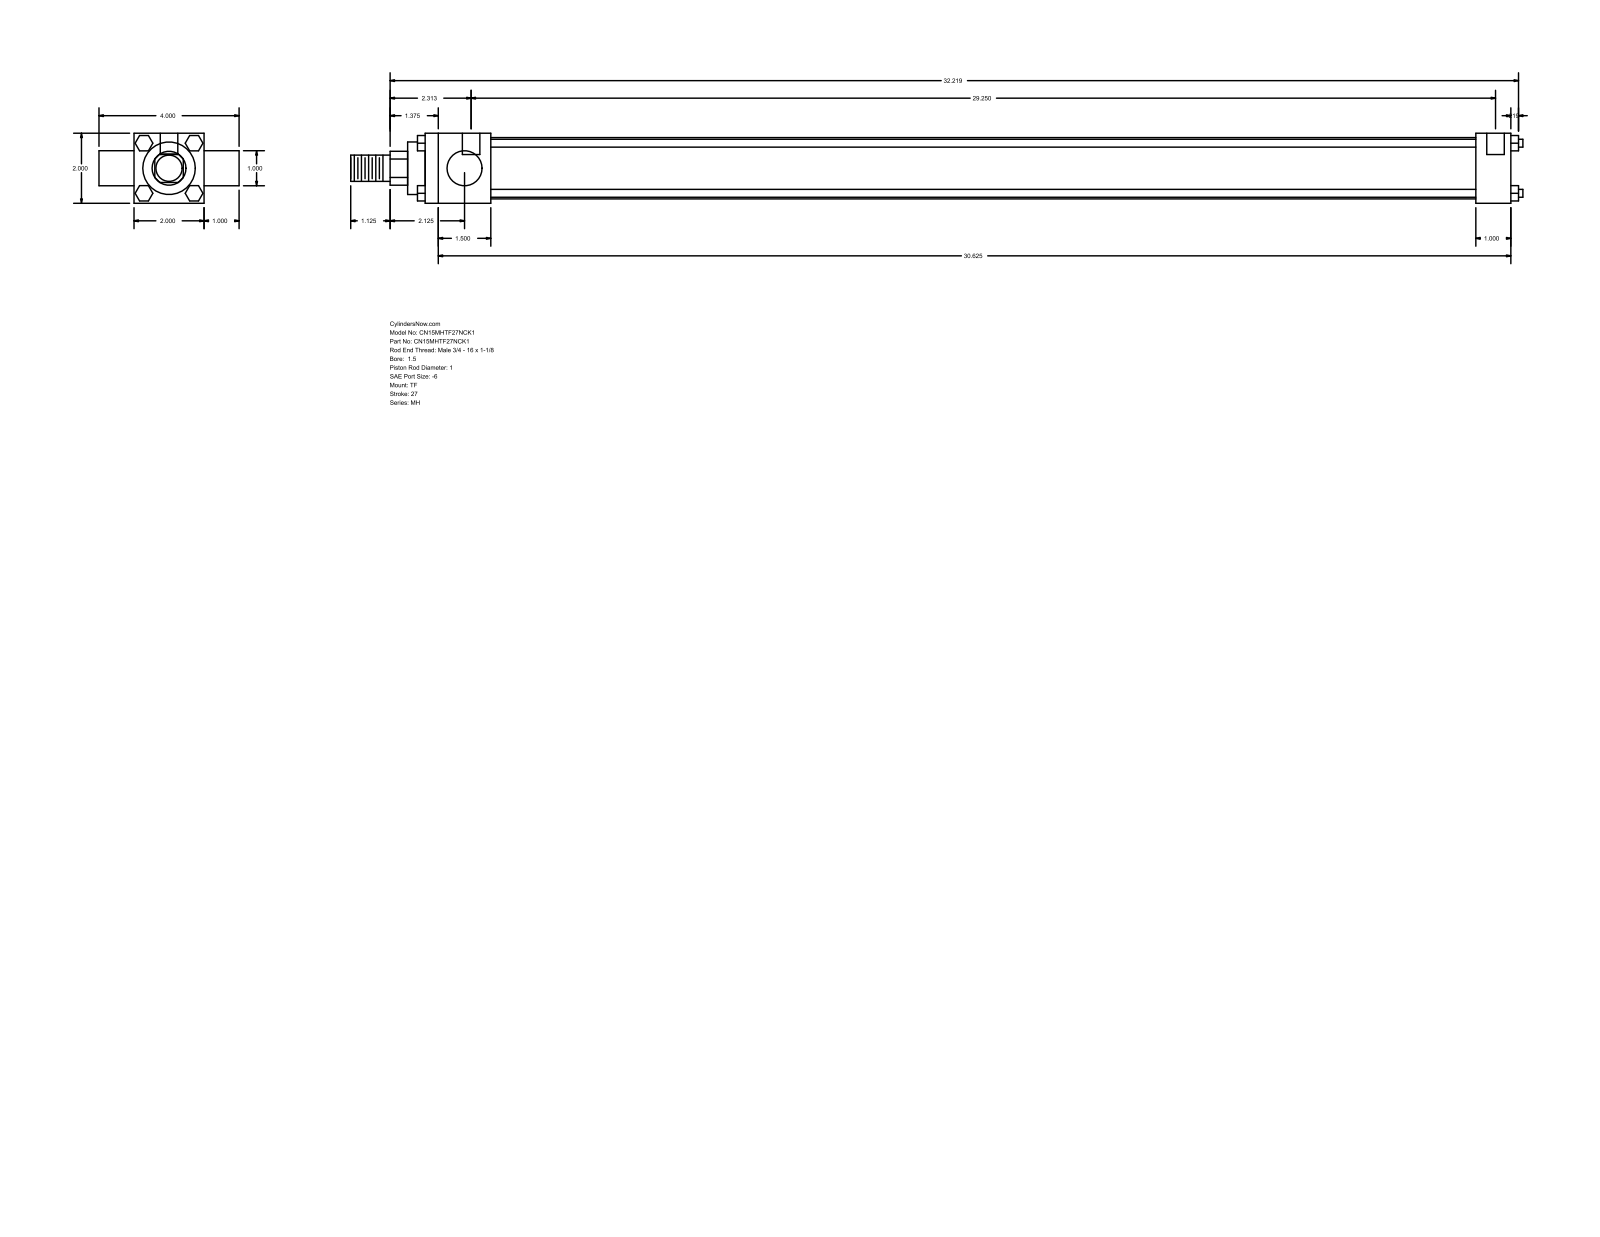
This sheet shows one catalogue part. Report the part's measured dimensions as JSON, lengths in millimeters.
{"part_name": "MH_TF__0150_1", "step_written_by": "GSSL Pune (CONFIG_CONTROL_DESIGN)", "units": "millimeters", "bodies": {"solids": 0, "faces": 120, "planar": 92, "cylindrical": 28, "other": 0}, "overall_size": [850.11, 101.6, 50.8], "round_holes": [[5.56, 3], [12.7, 2]], "round_bosses_or_shafts": [[5.71, 4], [25.4, 2], [44.45, 1], [38.1, 1], [19.05, 1]], "partial_cylinders_radius": [[12.29, 1]], "face_to_face_distances": [50.8, 25.4, 787.4, 76.2, 47.63, 739.77, 762, 714.37, 101.6, 12.7], "hole_center_spacings": [3.18, 742.95, 746.13]}
